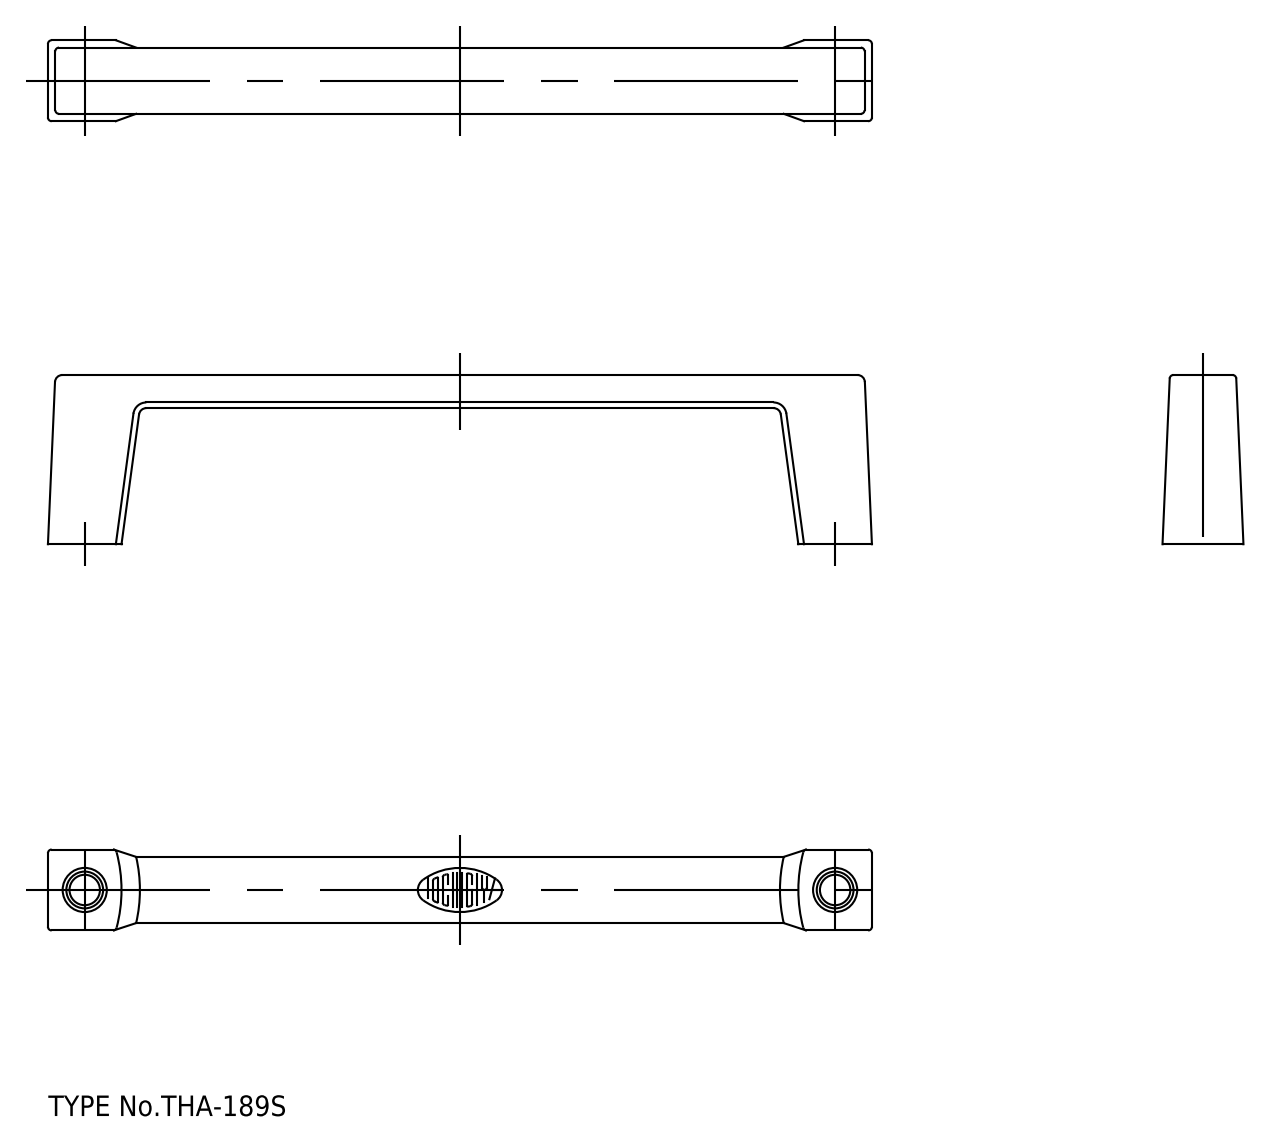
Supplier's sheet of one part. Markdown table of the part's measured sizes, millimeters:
| quantity | value |
| --- | --- |
| part name | pull |
| STEP written by | spGate 16.7.1 (AUTOMOTIVE_DESIGN) |
| units | millimeters |
| bodies | 1 solid, 40 faces (9 planar, 17 cylindrical, 14 other) |
| overall size | 112 × 23 × 11 |
| volume | 7 992 mm³ |
| surface area | 4 732 mm² |
| round holes (diameter × count) | 5 × 2 |
| partial cylindrical surfaces (radius × count) | 0.5 × 8, 1 × 2, 20.03 × 2, 20.03 × 1 |
| main face-to-face distances | 23, 13, 10 |
| hole center spacings | 102 |
